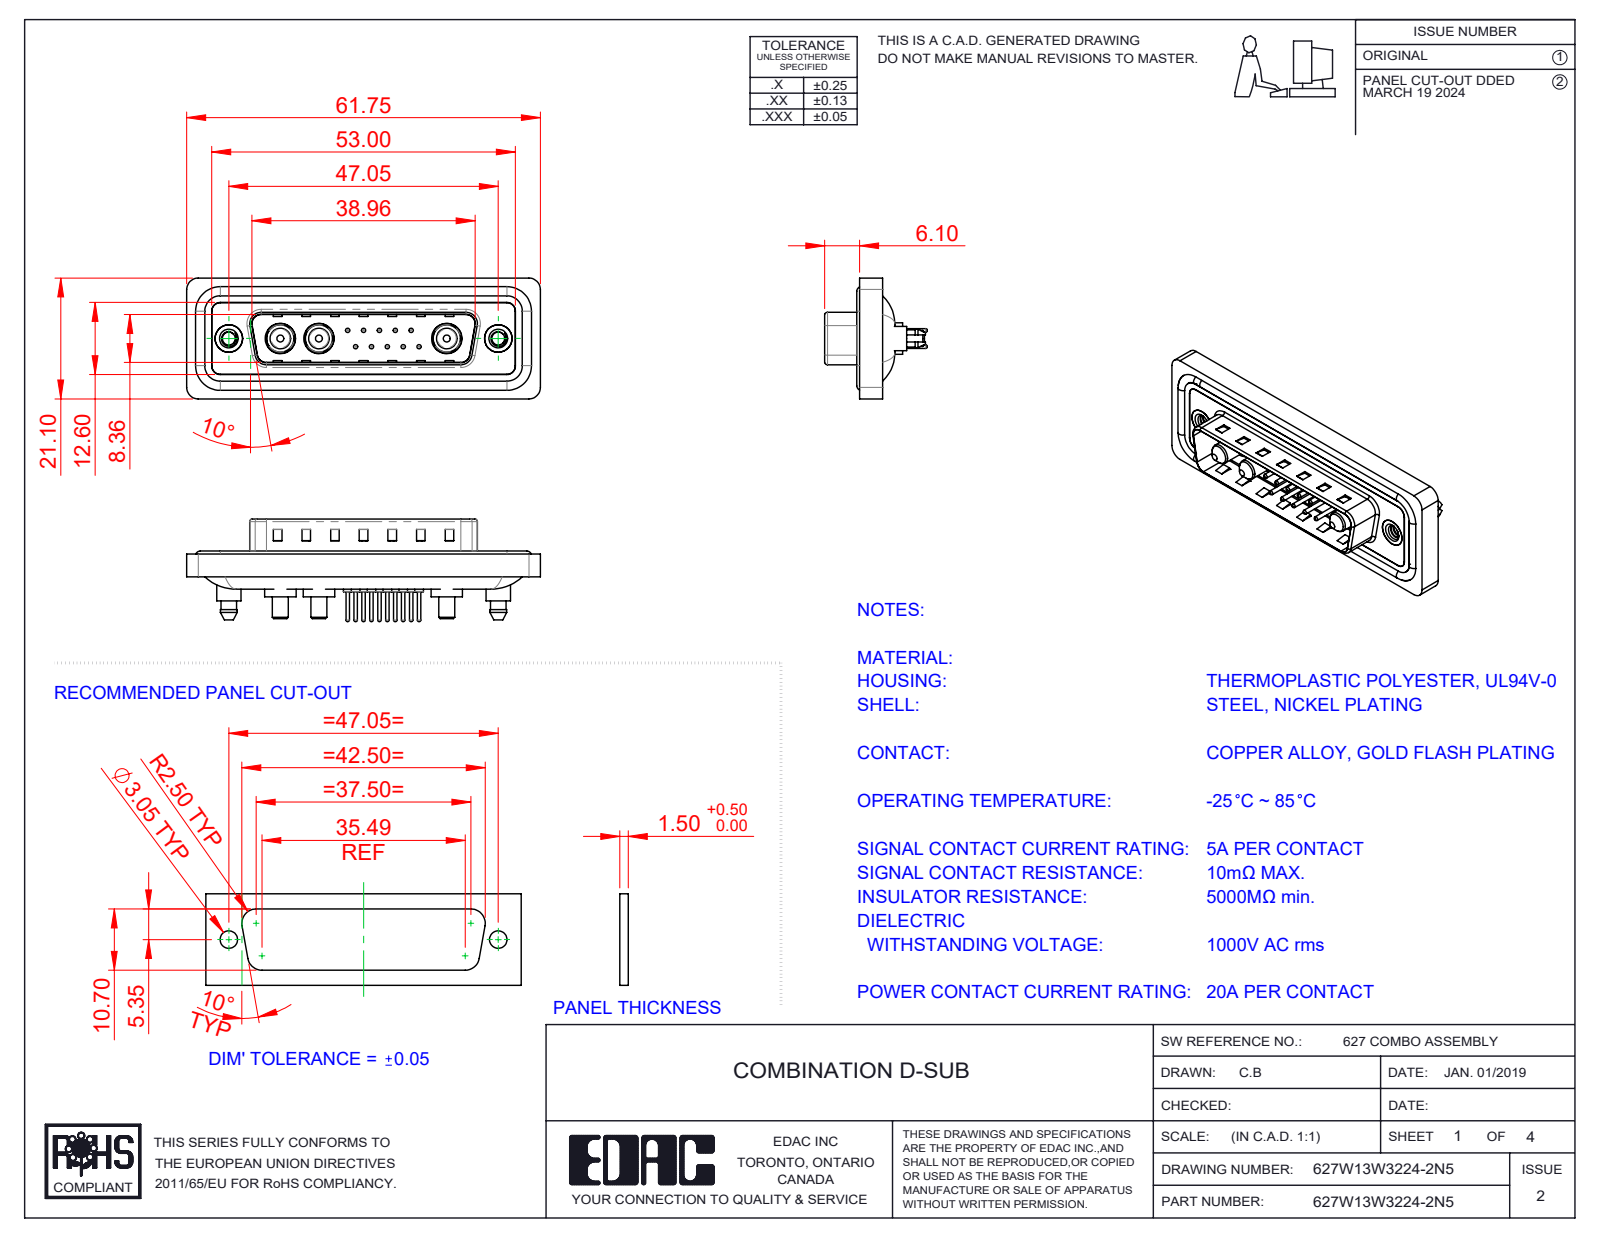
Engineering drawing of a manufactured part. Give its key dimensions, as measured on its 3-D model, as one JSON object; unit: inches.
{"part_name": "627Combo Housing_13W3; 627Combo Shell Front_25 Contacts; 627Combo Waterproof Housing_25 Contacts; 627Combo Threaded Boardlock_5 (+5 more)", "step_written_by": "SolidWorks 2023 (CONFIG_CONTROL_DESIGN)", "units": "inches", "bodies": {"solids": 23, "faces": 1020, "planar": 325, "cylindrical": 417, "other": 278}, "overall_size": [2.431, 0.831, 0.705], "volume_in3": 0.456, "surface_area_in2": 18.92, "round_holes": [[0.03, 10], [0.063, 10], [0.079, 10], [0.191, 3], [0.209, 3], [0.089, 2], [0.157, 2], [0.189, 2], [0.197, 2]], "round_bosses_or_shafts": [[0.059, 10], [0.024, 10], [0.063, 4], [0.217, 3], [0.205, 3], [0.187, 3], [0.148, 3], [0.142, 3]], "partial_cylinders_radius": [[0.059, 24], [0.079, 18], [0.063, 10], [0.02, 8], [0.01, 4], [0.024, 4], [0.026, 4], [0.035, 4]], "face_to_face_distances": [0.016, 0.059, 0.043, 0.063, 0.02, 0.122, 0.114, 0.032, 0.377, 0.161], "hole_center_spacings": [0.124, 0.109, 0.198, 0.218, 0.295, 0.198, 0.327, 0.398]}
